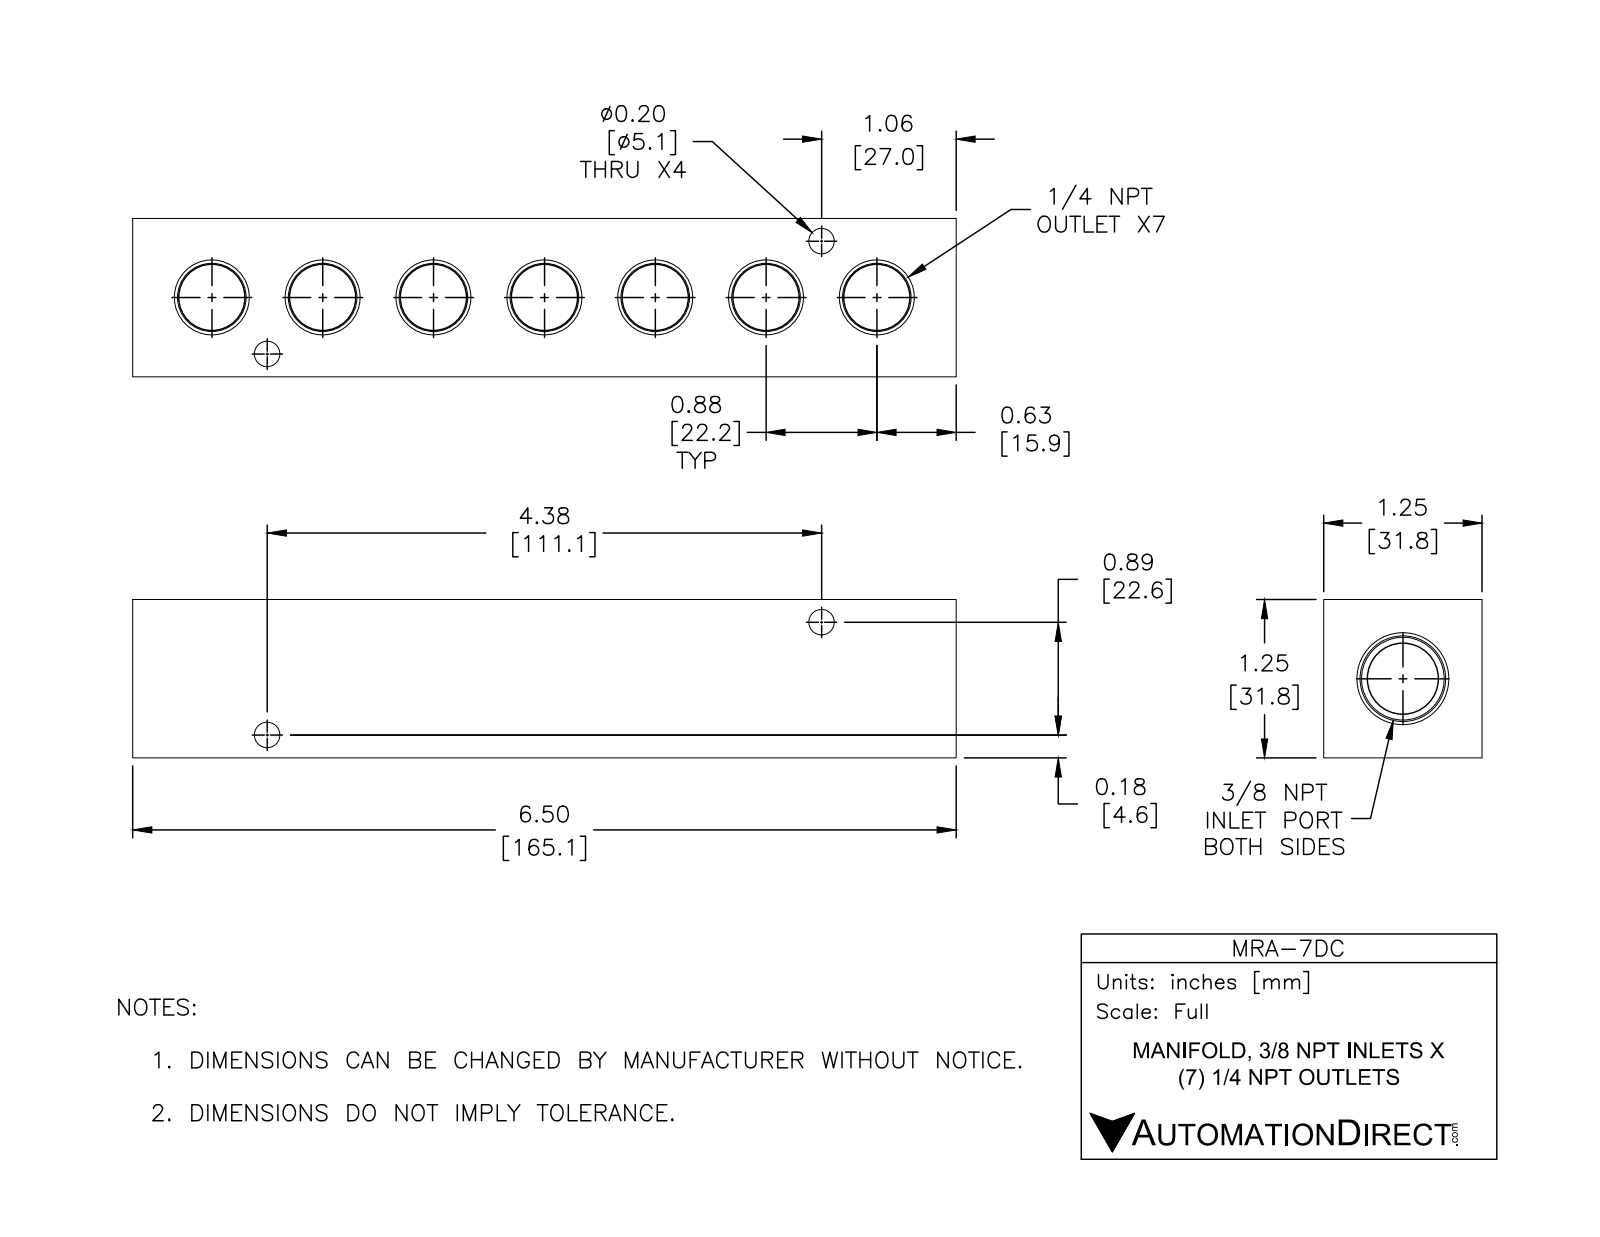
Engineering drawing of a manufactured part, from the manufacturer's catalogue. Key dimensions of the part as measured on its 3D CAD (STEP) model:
Part name (STEP PRODUCT): MRA-7DC
STEP written by: SolidWorks 2015 (CONFIG_CONTROL_DESIGN)
Units: inches
Bodies: 1 solid, 90 faces (22 planar, 32 cylindrical, 36 other)
Overall size (bounding box): 6.5 × 1.25 × 1.25
Volume: 7.741 in³ · Surface area: 50.95 in²
Round holes (diameter × count): ⌀0.2 ×4, ⌀0.562 ×1
Partial cylindrical surfaces — rounded edges, fillets, slot ends (radius × count): R0.219 ×7
Main face-to-face distances: 1.25, 6.5, 0.86, 0.39, 0.41, 6.09, 5.68
Hole centre spacings: 4.464
